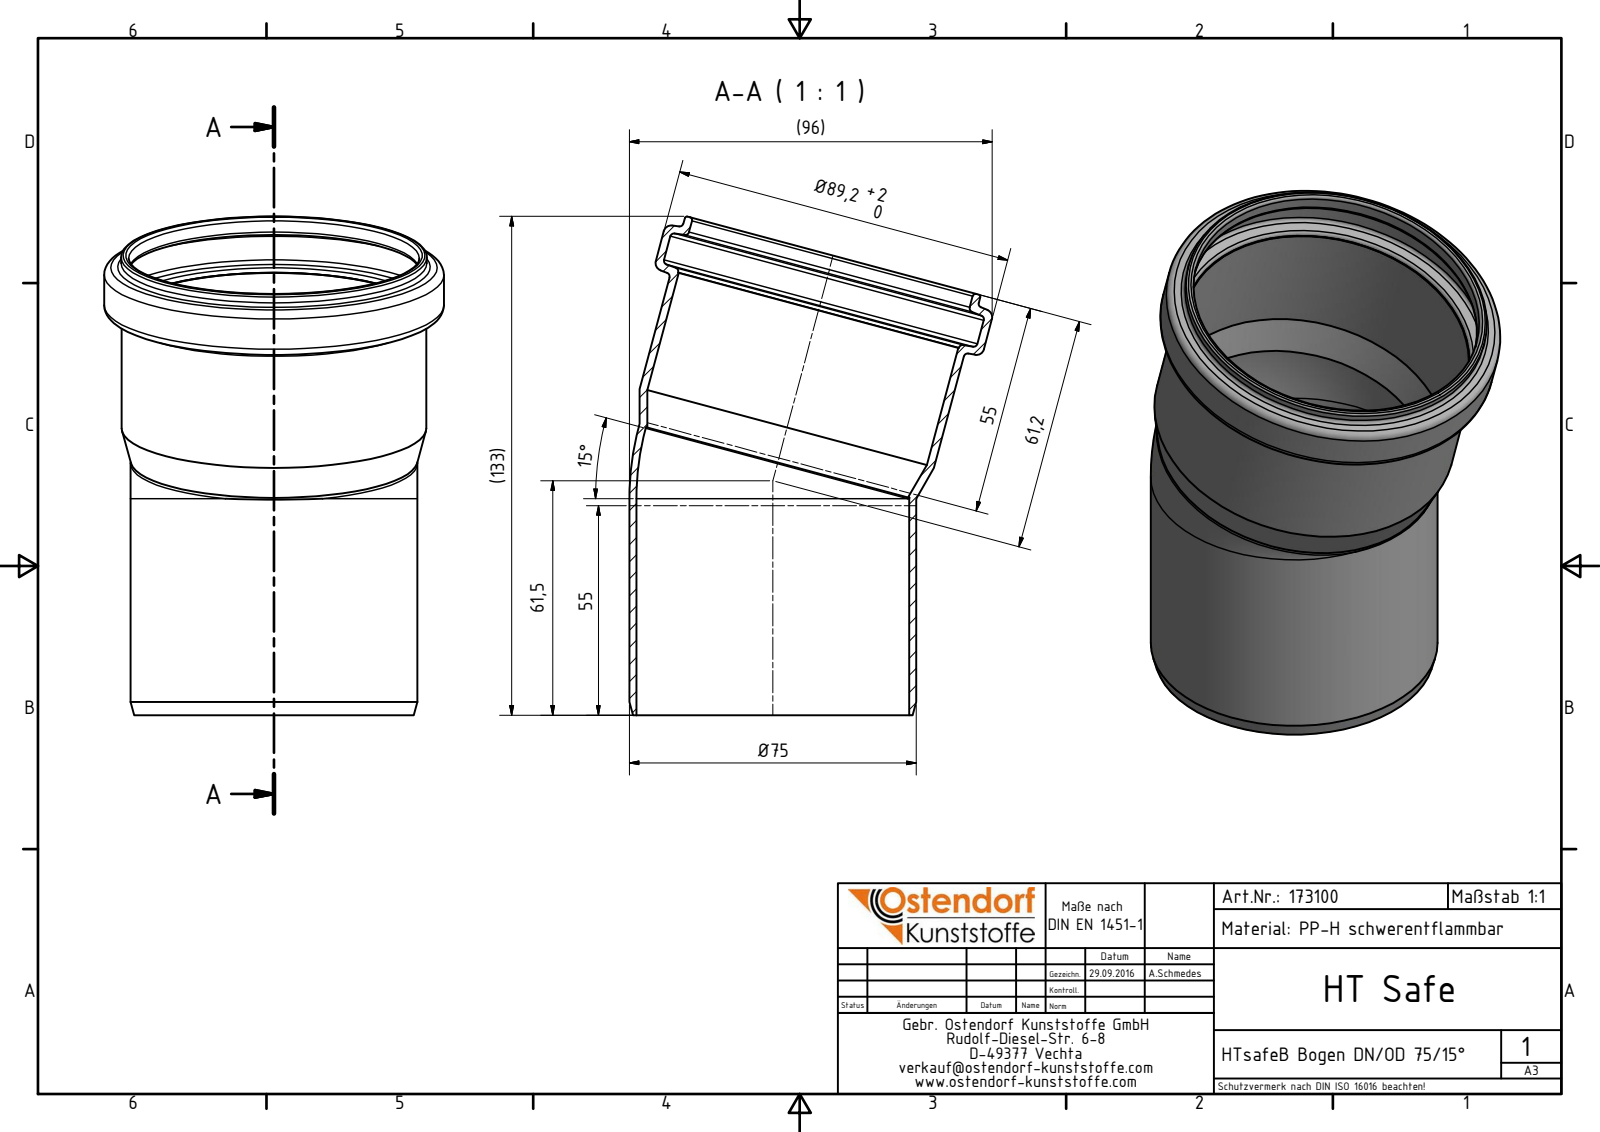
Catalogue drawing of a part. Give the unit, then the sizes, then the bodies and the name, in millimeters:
Units: millimetres
Overall size (bounding box): 130.89 × 95.27 × 89.2
Round holes (diameter × count): ⌀71.61 ×2, ⌀76 ×1, ⌀76.3 ×1, ⌀85.2 ×1
Round bosses / shafts (diameter × count): ⌀75.3 ×2, ⌀89.2 ×1, ⌀80.3 ×1, ⌀80 ×1
Main face-to-face distances: 56.22, 41.33, 14.89
Volume: 59 760 mm³ · Surface area: 62 851 mm²
Bodies: 1 solid, 34 faces (4 planar, 11 cylindrical, 19 other)
Part name (STEP PRODUCT): 173100 HTsafeB DN_OD 75_15°
STEP written by: Autodesk Inventor 2016 (AUTOMOTIVE_DESIGN)
